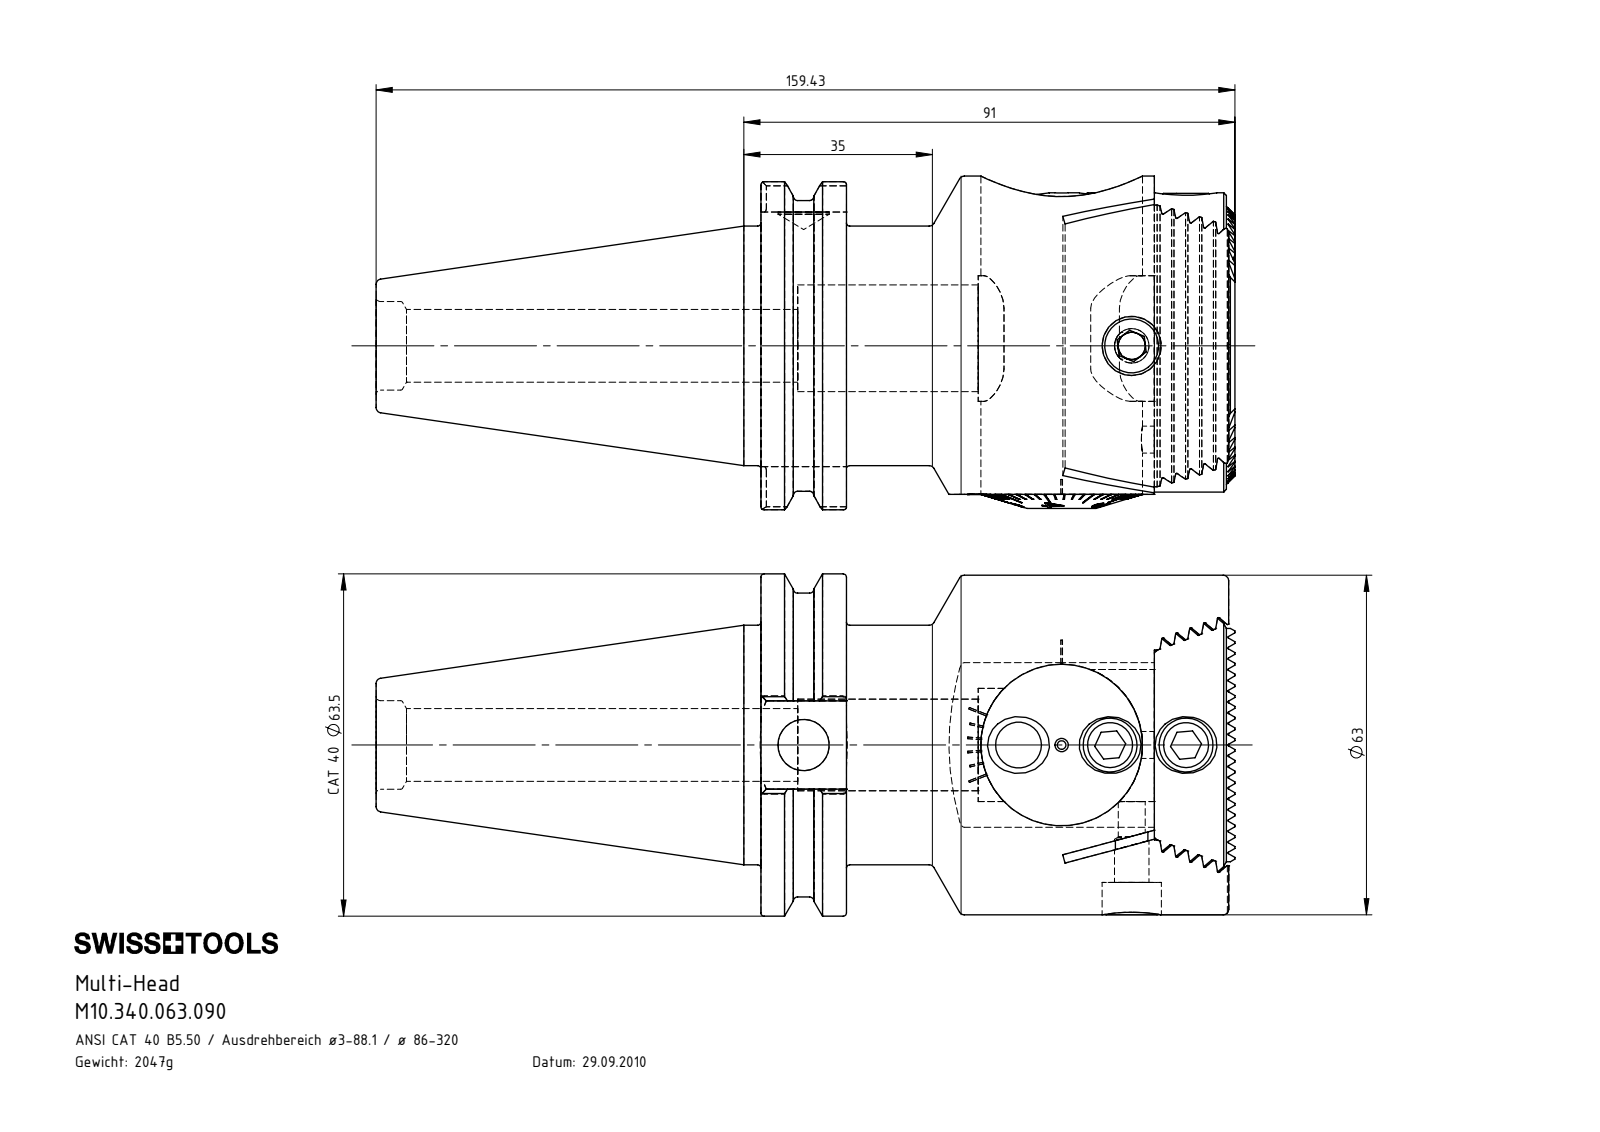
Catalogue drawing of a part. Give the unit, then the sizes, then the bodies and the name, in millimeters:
Units: millimetres
Overall size (bounding box): 159.43 × 63.5 × 61.91
Round holes (diameter × count): ⌀4.2 ×5, ⌀8.5 ×4, ⌀6.8 ×3, ⌀11 ×3, ⌀5 ×2, ⌀20 ×2, ⌀1 ×1, ⌀1.6 ×1, ⌀3.3 ×1, ⌀6.4 ×1, ⌀8 ×1, ⌀9.5 ×1
Round bosses / shafts (diameter × count): ⌀10 ×3, ⌀63.5 ×1, ⌀63 ×1, ⌀56.36 ×1, ⌀44.45 ×1, ⌀30 ×1, ⌀29.98 ×1, ⌀29.9 ×1
Partial cylindrical surfaces — rounded edges, fillets, slot ends (radius × count): R0.14 ×21, R0.2 ×20, R0.8 ×8, R6 ×6, R4 ×2, R8.5 ×2, R31 ×2, R2 ×1
Main face-to-face distances: 2.38, 7.15, 57.15, 1.73, 15.87, 73.02, 4.76, 8.66, 5.2, 4.77
Hole centre spacings: 16.73, 16.77, 17.4, 17.97, 18.03, 20.52, 20.59, 24
Volume: 263 138 mm³ · Surface area: 74 904 mm²
Bodies: 15 solids, 926 faces (549 planar, 180 cylindrical, 197 other)
Part name (STEP PRODUCT): A55-BG2.015.007_A; DIN 3771 - 25x1.5; MH1-BG2.001.056_D; ISO 4026 - M10 x 16_PreviewCfg (+8 more)
STEP written by: SolidWorks 2017 (AUTOMOTIVE_DESIGN)
